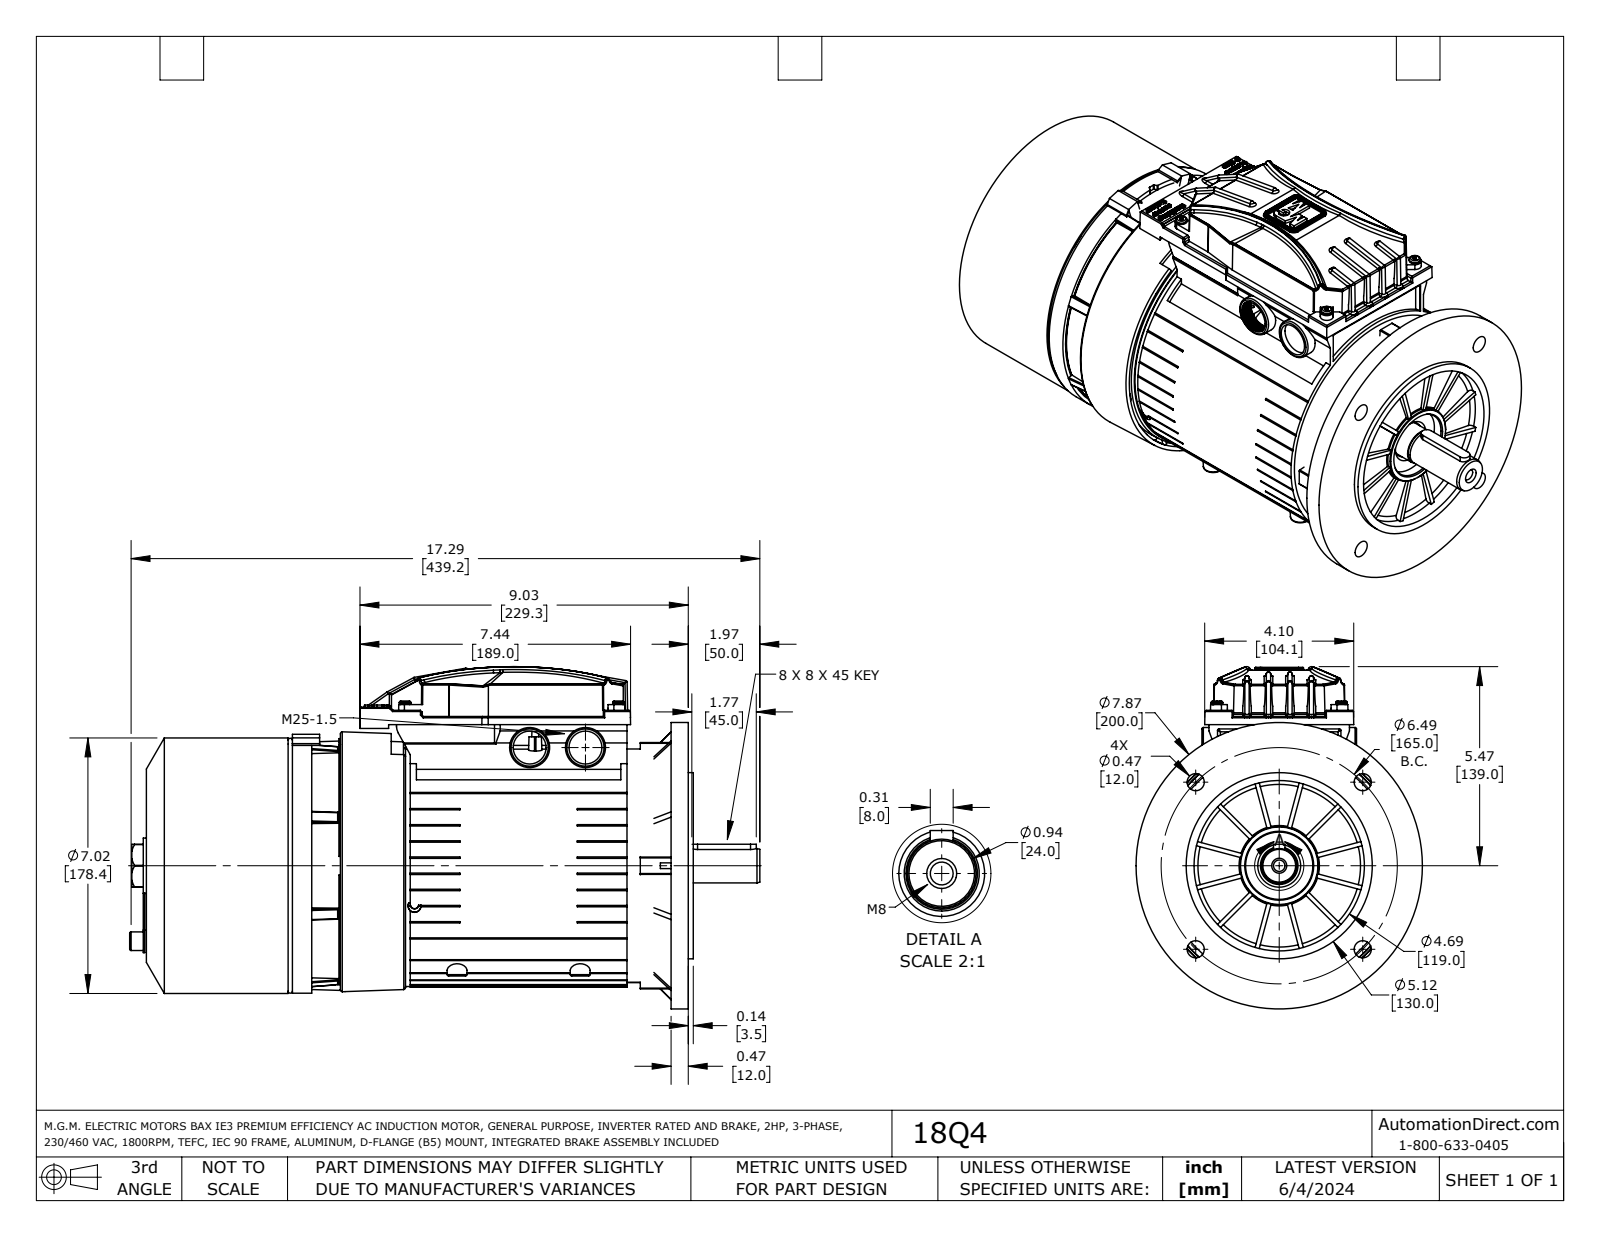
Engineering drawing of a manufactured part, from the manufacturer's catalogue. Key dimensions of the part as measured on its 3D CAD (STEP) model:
Part name (STEP PRODUCT): 18Q4
STEP written by: SolidWorks 2021 (AUTOMOTIVE_DESIGN)
Units: inches
Bodies: 16 solids, 3551 faces (1548 planar, 820 cylindrical, 1183 other)
Overall size (bounding box): 17.33 × 9.41 × 7.874
Volume: 541.8 in³ · Surface area: 1 313 in²
Round holes (diameter × count): ⌀0.13 ×14, ⌀0.315 ×6, ⌀0.098 ×5, ⌀0.472 ×5, ⌀0.165 ×4, ⌀0.177 ×4, ⌀0.106 ×2, ⌀0.256 ×2, ⌀0.906 ×2, ⌀0.512 ×1, ⌀1.033 ×1, ⌀1.063 ×1
Round bosses / shafts (diameter × count): ⌀0.138 ×6, ⌀0.197 ×5, ⌀0.315 ×4, ⌀0.276 ×3, ⌀1.102 ×2, ⌀0.453 ×2, ⌀7.874 ×1, ⌀7.087 ×1
Partial cylindrical surfaces — rounded edges, fillets, slot ends (radius × count): R0.059 ×47, R0.008 ×32, R0.004 ×24, R0.039 ×24, R0.02 ×22, R0.031 ×22, R0.033 ×16, R0.033 ×16
Main face-to-face distances: 0.472, 14.902, 14.429, 0.197, 0.276, 14.705, 0.118, 0.106, 0.157, 0.256
Hole centre spacings: 0.472, 2.437, 5.875, 0.818, 2.903, 3.707, 2.711, 2.794
